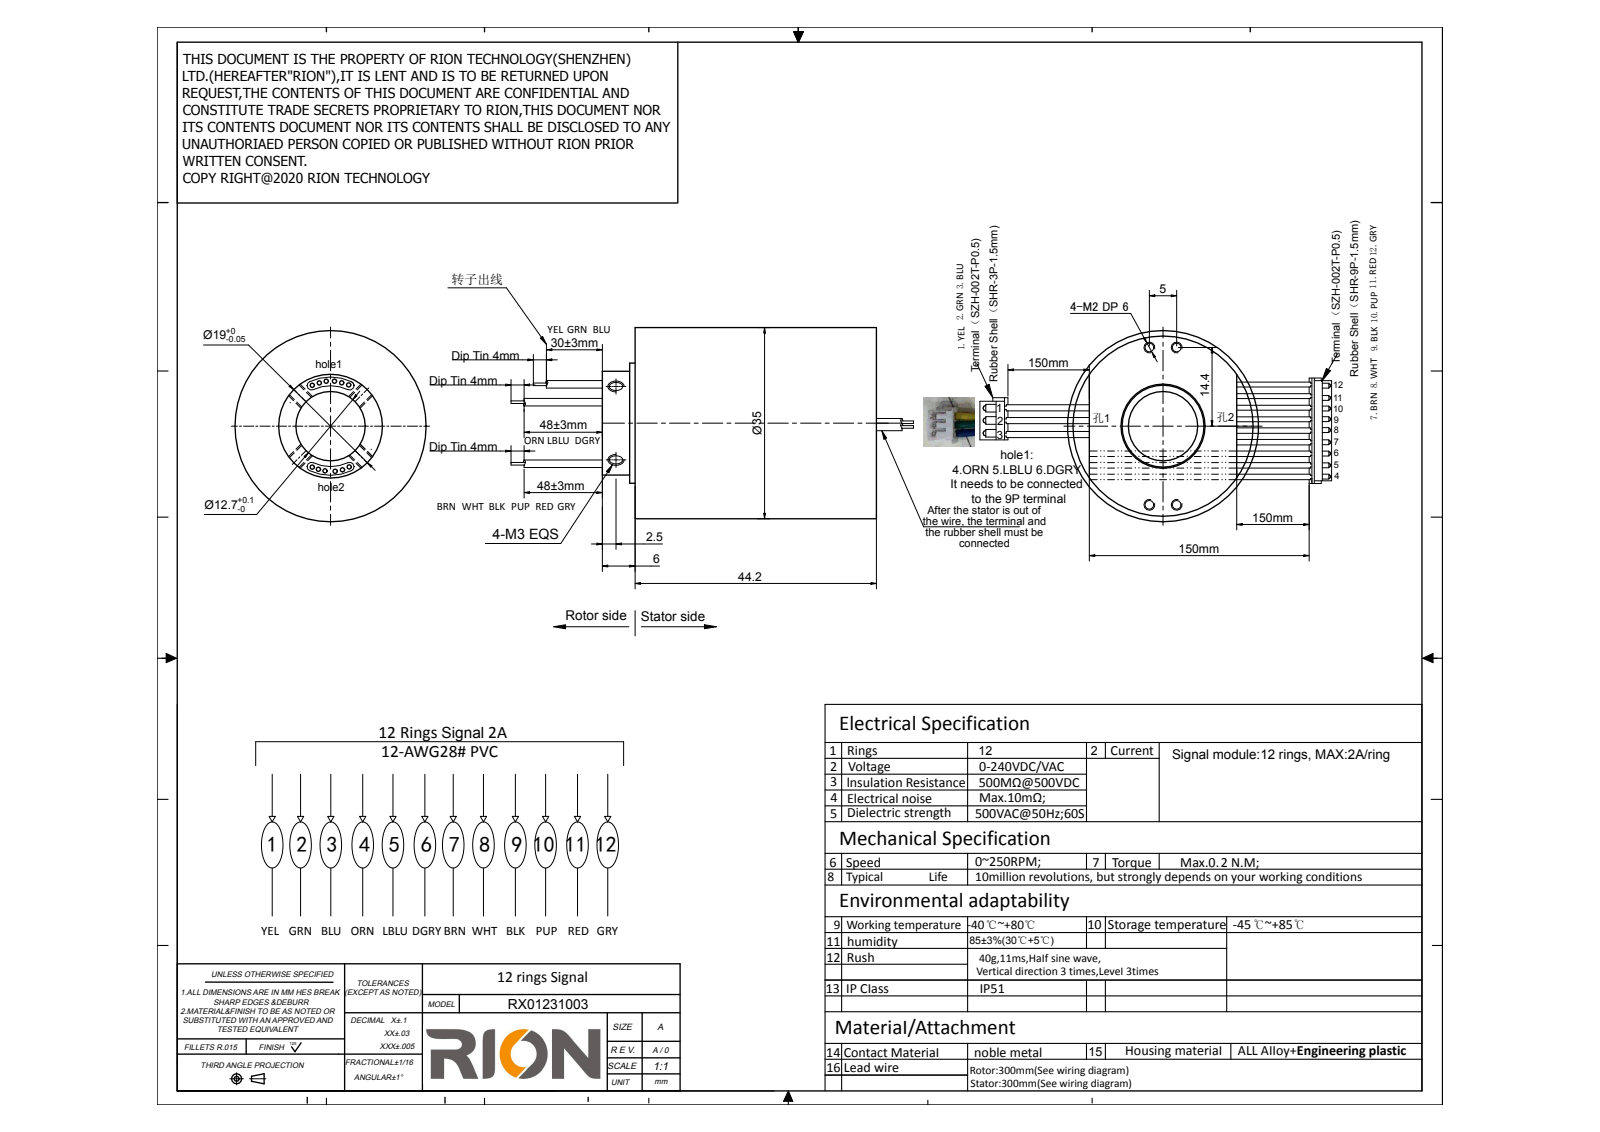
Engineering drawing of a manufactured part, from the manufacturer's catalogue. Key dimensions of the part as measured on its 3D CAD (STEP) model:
Part name (STEP PRODUCT): RX01231003
STEP written by: SolidWorks 2014 (CONFIG_CONTROL_DESIGN)
Units: millimetres
Bodies: 1 solid, 130 faces (36 planar, 86 cylindrical, 8 other)
Overall size (bounding box): 69.2 × 35 × 35
Volume: 37 910 mm³ · Surface area: 10 105 mm²
Round holes (diameter × count): ⌀1.6 ×4, ⌀2.5 ×2, ⌀12.7 ×1, ⌀32.2 ×1
Round bosses / shafts (diameter × count): ⌀0.8 ×24, ⌀35 ×1, ⌀32 ×1, ⌀22 ×1, ⌀19 ×1
Partial cylindrical surfaces — rounded edges, fillets, slot ends (radius × count): R0.85 ×4, R4.57 ×2, R6.26 ×2
Main face-to-face distances: 44.2, 50.2, 6, 45.2, 1, 5, 0.5, 49.7, 43.7, 44.7
Hole centre spacings: 14.62, 5, 28.8, 29.23
